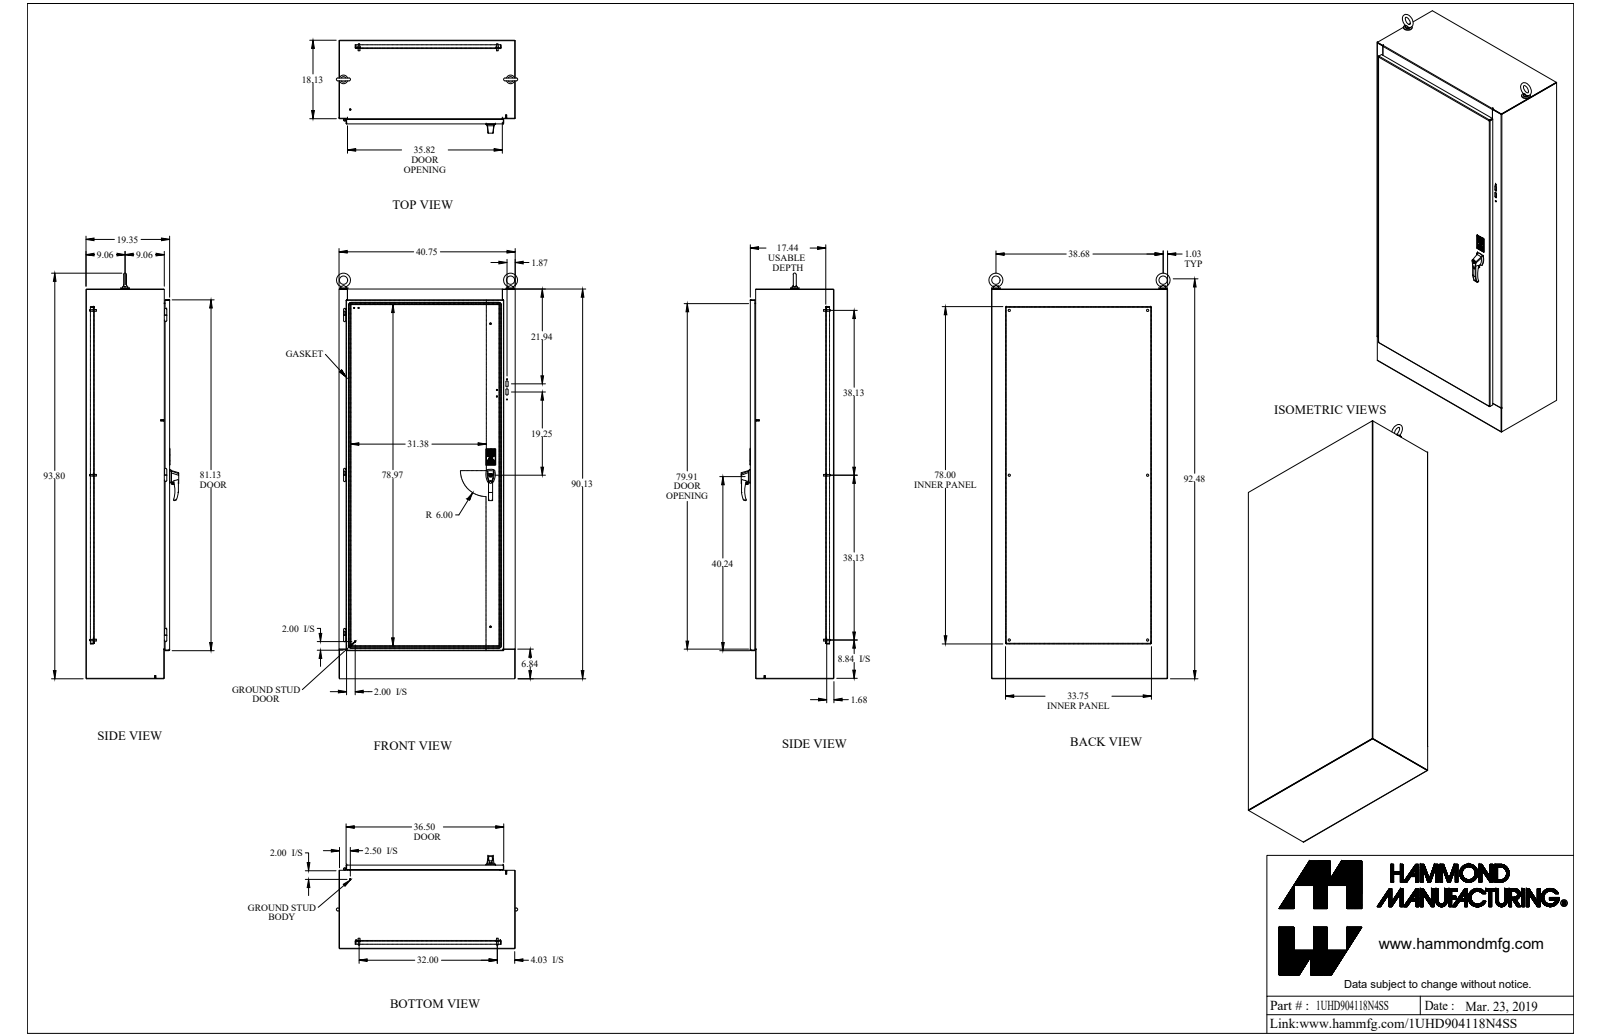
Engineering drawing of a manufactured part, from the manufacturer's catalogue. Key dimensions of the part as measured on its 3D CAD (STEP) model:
Part name (STEP PRODUCT): 1UHD904118N4SS
STEP written by: SolidWorks 2018 (AUTOMOTIVE_DESIGN)
Units: inches
Bodies: 106 solids, 1969 faces (1108 planar, 525 cylindrical, 336 other)
Overall size (bounding box): 93.544 × 41.932 × 21.464
Volume: 1 724 in³ · Surface area: 34 374 in²
Round holes (diameter × count): ⌀0.35 ×7, ⌀0.196 ×6, ⌀0.307 ×6, ⌀0.563 ×6, ⌀0.25 ×5, ⌀0.156 ×4, ⌀0.281 ×4, ⌀0.445 ×4, ⌀0.313 ×3, ⌀0.167 ×2, ⌀0.189 ×2, ⌀0.255 ×2
Round bosses / shafts (diameter × count): ⌀0.25 ×11, ⌀1 ×8, ⌀0.375 ×7, ⌀0.65 ×6, ⌀0.332 ×6, ⌀0.19 ×4, ⌀0.625 ×3, ⌀0.5 ×3
Partial cylindrical surfaces — rounded edges, fillets, slot ends (radius × count): R0.125 ×27, R0.048 ×24, R0.143 ×24, R0.5 ×23, R0.06 ×19, R0.25 ×19, R0.017 ×16, R0.032 ×12
Main face-to-face distances: 0.095, 19.254, 40.655, 19.159, 19.349, 0.125, 1.907, 1.812, 17.348, 17.443
Hole centre spacings: 32, 7.433, 7.467, 7.5, 12.875, 14.9, 30.461, 33.937
